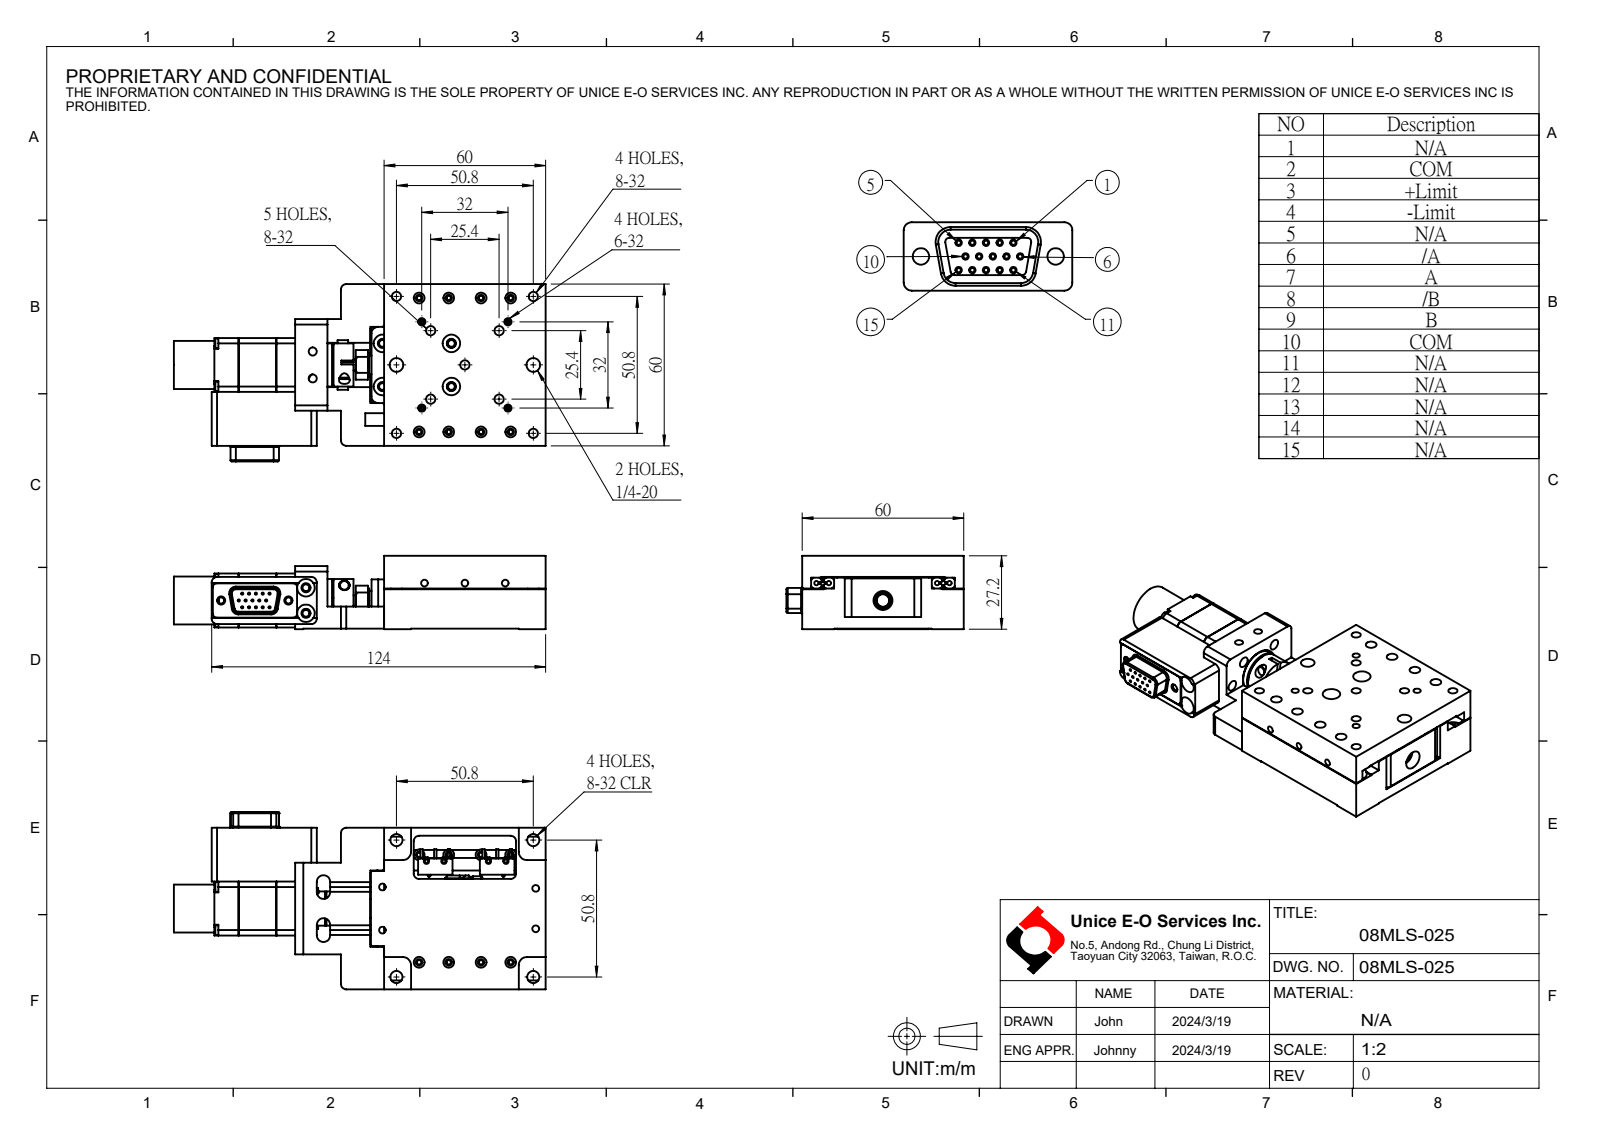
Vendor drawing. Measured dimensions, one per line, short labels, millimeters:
name: 08MLS-025
written by: SolidWorks 2022 (CONFIG_CONTROL_DESIGN)
unit: mm
bodies: 0 solids, 439 faces (242 planar, 180 cylindrical, 17 other)
size: 138 × 65.83 × 27.2
holes: 18× ⌀4, 15× ⌀0.8, 9× ⌀2.5, 9× ⌀3.45, 8× ⌀6.5, 4× ⌀2, 4× ⌀2.71, 4× ⌀4.5, 4× ⌀7.94, 3× ⌀3, 2× ⌀2.26, 2× ⌀2.6
bosses: 4× ⌀3.6, 2× ⌀4, 1× ⌀17.8, 1× ⌀16, 1× ⌀14.8, 1× ⌀12, 1× ⌀8, 1× ⌀6
rounds: 18× R2, 9× R2.5, 8× R0.5, 4× R1, 4× R1.5, 4× R3, 2× R1.8, 1× R6.25
face distances: 19.2, 27, 7.8, 60, 4, 4.3, 15.85, 44.15, 20, 18.9
hole spacings: 2.84, 4.58, 5.08, 2.54, 17.96, 40.16, 6.84, 25.4
